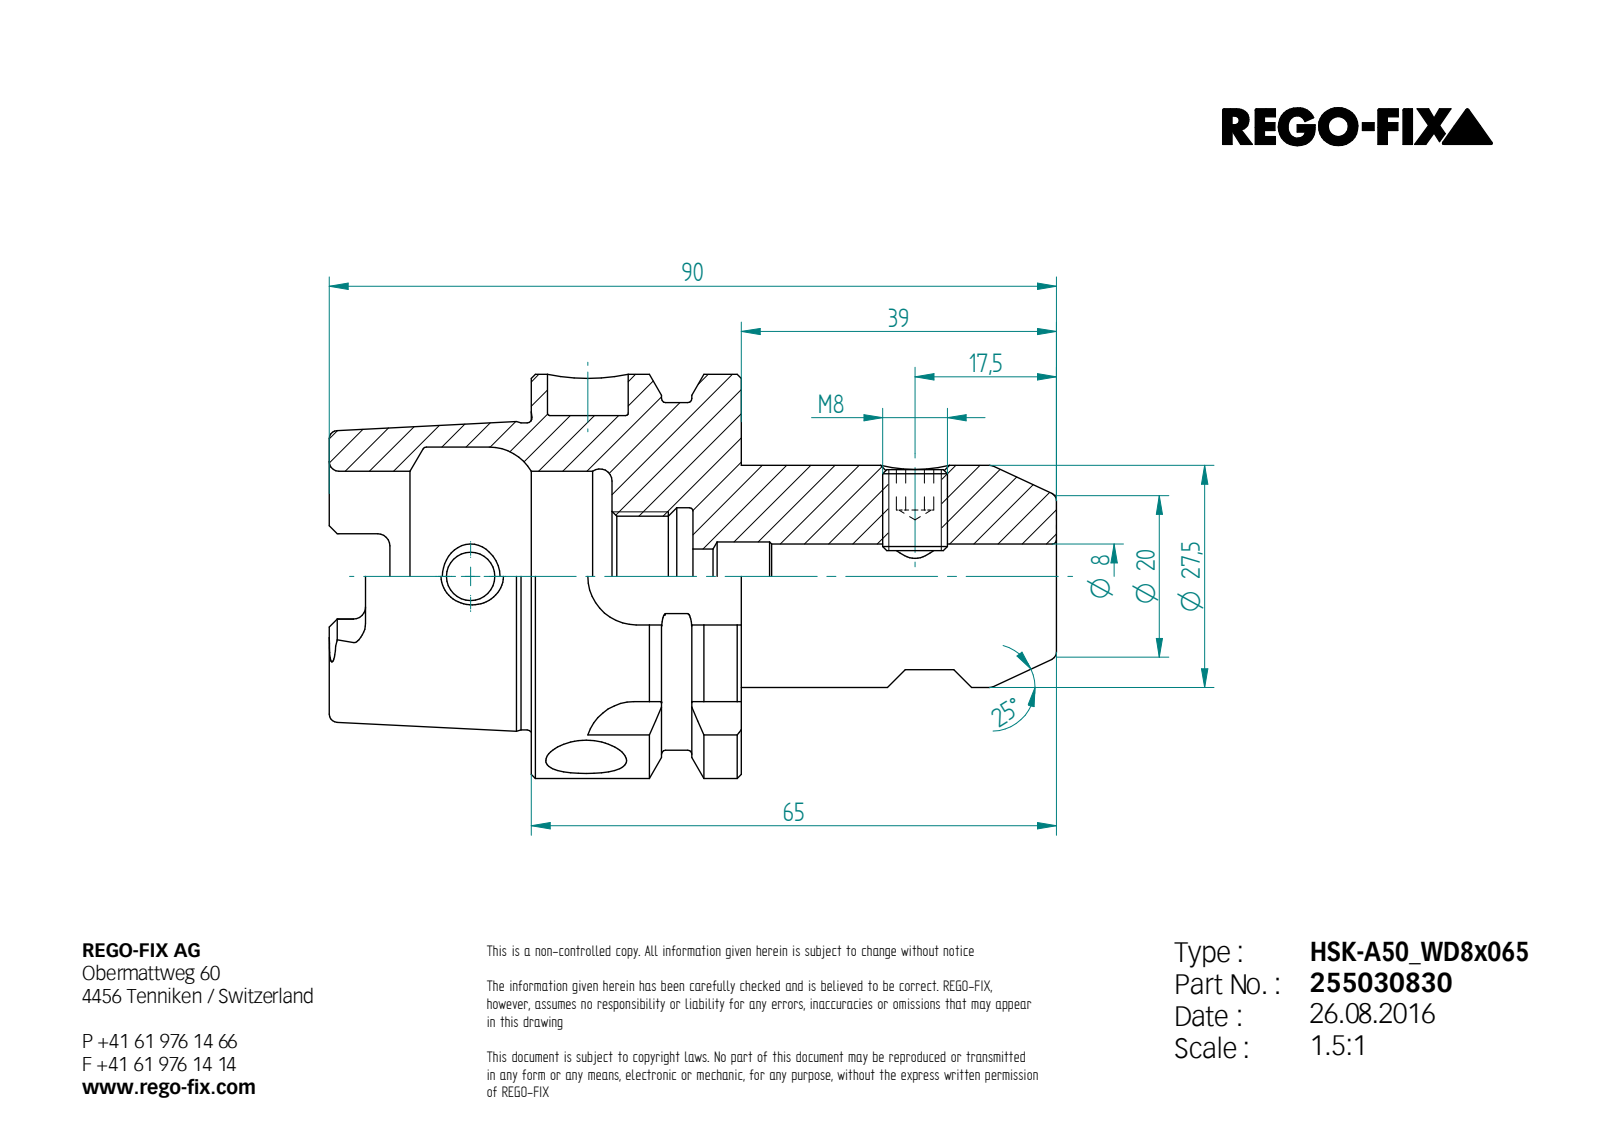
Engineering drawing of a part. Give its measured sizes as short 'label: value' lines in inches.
written by: Unknown (AUTOMOTIVE_DESIGN)
unit: in
bodies: 2 solids, 152 faces (63 planar, 36 cylindrical, 53 other)
size: 3.543 × 1.969 × 1.969
volume: 4.17 in³; area: 30.68 in²
holes: 2× ⌀0.394, 1× ⌀0.236, 1× ⌀0.262, 1× ⌀0.268, 1× ⌀0.315, 1× ⌀0.335, 1× ⌀0.587, 1× ⌀0.669, 1× ⌀1.024, 1× ⌀1.26
bosses: 1× ⌀1.969, 1× ⌀1.693, 1× ⌀1.496, 1× ⌀1.083, 1× ⌀0.315
rounds: 6× R0.059, 4× R0.094, 4× R0.236
face distances: 1.024, 0.394, 1.772, 0.63, 2.559, 2.165, 1.535, 1.654, 0.984, 1.378
hole spacings: 1.594
